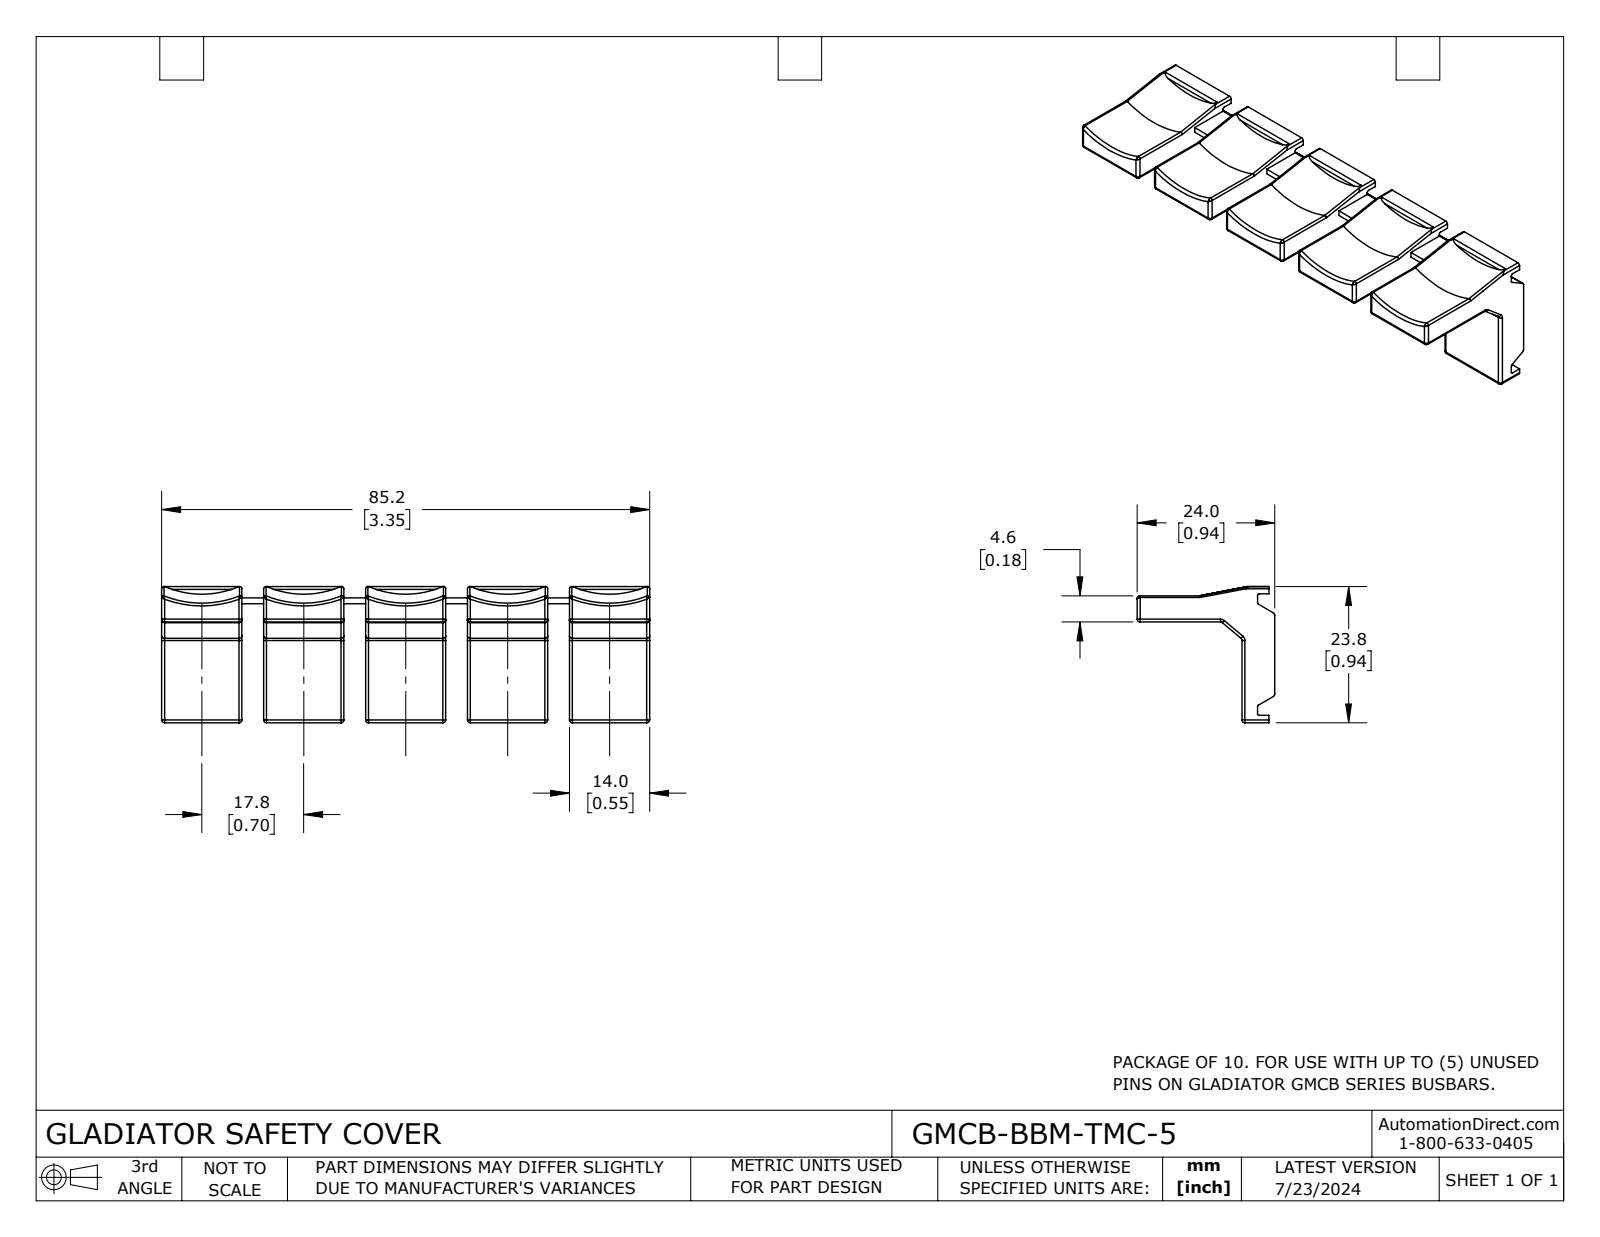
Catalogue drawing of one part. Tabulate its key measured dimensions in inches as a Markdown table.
| quantity | value |
| --- | --- |
| part name | GMCB-BBM-TMC-5 |
| STEP written by | SolidWorks 2023 (CONFIG_CONTROL_DESIGN) |
| units | inches |
| bodies | 1 solid, 298 faces (98 planar, 130 cylindrical, 70 other) |
| overall size | 3.354 × 0.945 × 0.937 |
| volume | 0.839 in³ |
| surface area | 13.89 in² |
| partial cylindrical surfaces (radius × count) | 0.02 × 57, 0.012 × 14, 0.016 × 10, 0.709 × 5 |
| main face-to-face distances | 0.701, 1.402, 0.224, 0.551, 2.102, 1.252, 0.15, 1.953, 0.85, 2.803 |
